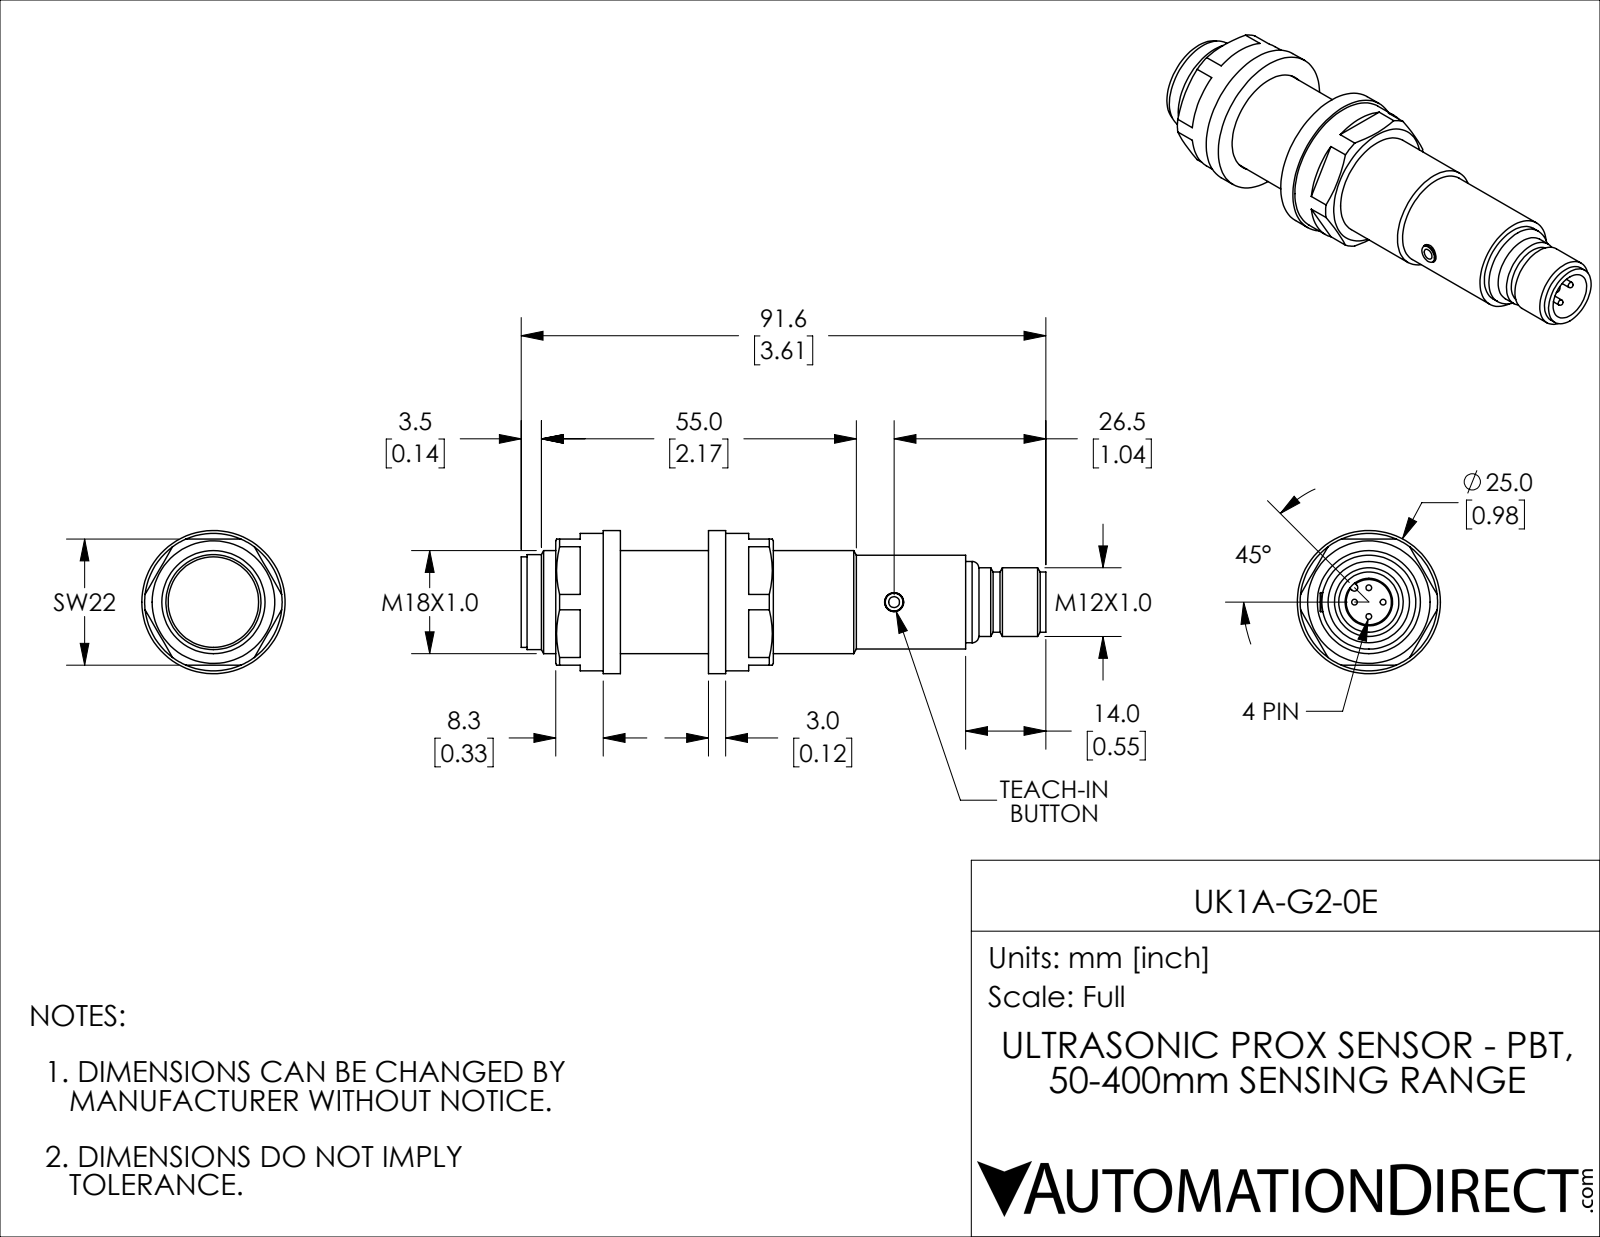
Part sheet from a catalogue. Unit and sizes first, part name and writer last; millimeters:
Units: millimetres
Overall size (bounding box): 91.6 × 25 × 25
Round holes (diameter × count): ⌀3.3 ×1, ⌀8.3 ×1, ⌀18 ×1, ⌀18.2 ×1
Round bosses / shafts (diameter × count): ⌀1 ×4, ⌀25 ×1, ⌀24 ×1, ⌀16.6 ×1, ⌀16.4 ×1, ⌀15.8 ×1, ⌀14.2 ×1, ⌀12 ×1
Partial cylindrical surfaces — rounded edges, fillets, slot ends (radius × count): R0.6 ×1
Main face-to-face distances: 3, 18.4, 21.4, 15.4, 22, 8.3, 11.3, 26.7, 29.7, 14.3
Volume: 24 200 mm³ · Surface area: 10 330 mm²
Bodies: 6 solids, 123 faces (43 planar, 49 cylindrical, 31 other)
Part name (STEP PRODUCT): UK1A-G2-0E
STEP written by: SolidWorks 2018 (AUTOMOTIVE_DESIGN)
